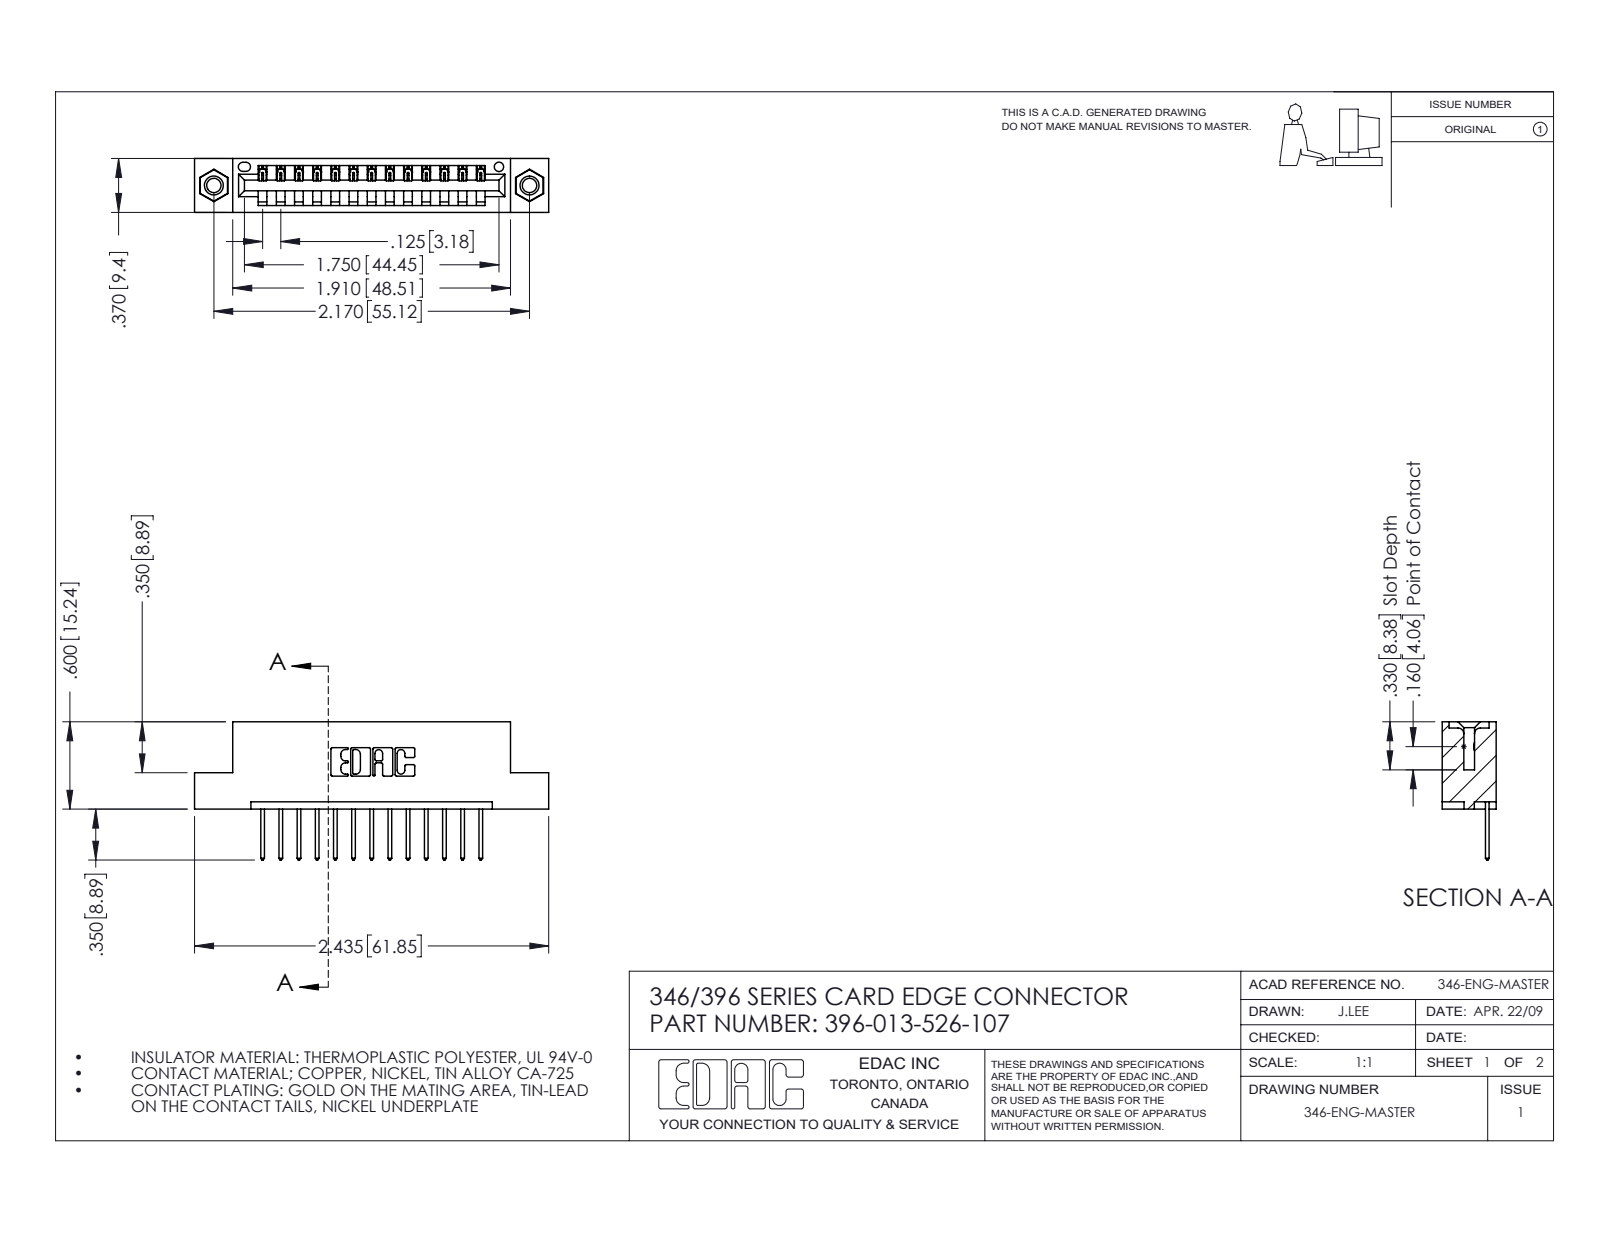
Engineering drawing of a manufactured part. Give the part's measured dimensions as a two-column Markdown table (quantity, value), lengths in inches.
| quantity | value |
| --- | --- |
| part name | 345-292-001_345-293-126; 346 Part_Flush Mounting Lugs - 0.156 Dia-TI; 396-013-526-107; 345-250-001_345-250-005-103 |
| STEP written by | SolidWorks 2016 (CONFIG_CONTROL_DESIGN) |
| units | inches |
| bodies | 16 solids, 936 faces (628 planar, 292 cylindrical, 16 other) |
| overall size | 2.435 × 0.95 × 0.37 |
| volume | 0.348 in³ |
| surface area | 10.59 in² |
| round holes (diameter × count) | 0.098 × 2, 0.125 × 2, 0.156 × 2, 0.064 × 1 |
| round bosses / shafts (diameter × count) | 0.155 × 2 |
| partial cylindrical surfaces (radius × count) | 0.006 × 26, 0.01 × 26, 0.01 × 22, 0.007 × 6, 0.031 × 6, 0.026 × 3, 0.031 × 2, 0.04 × 2 |
| main face-to-face distances | 0.25, 0.048, 0.322, 0.37, 0.072, 0.298, 0.025, 0.148, 0.222, 0.1 |
| hole center spacings | 0.246, 1.964, 2.17 |
